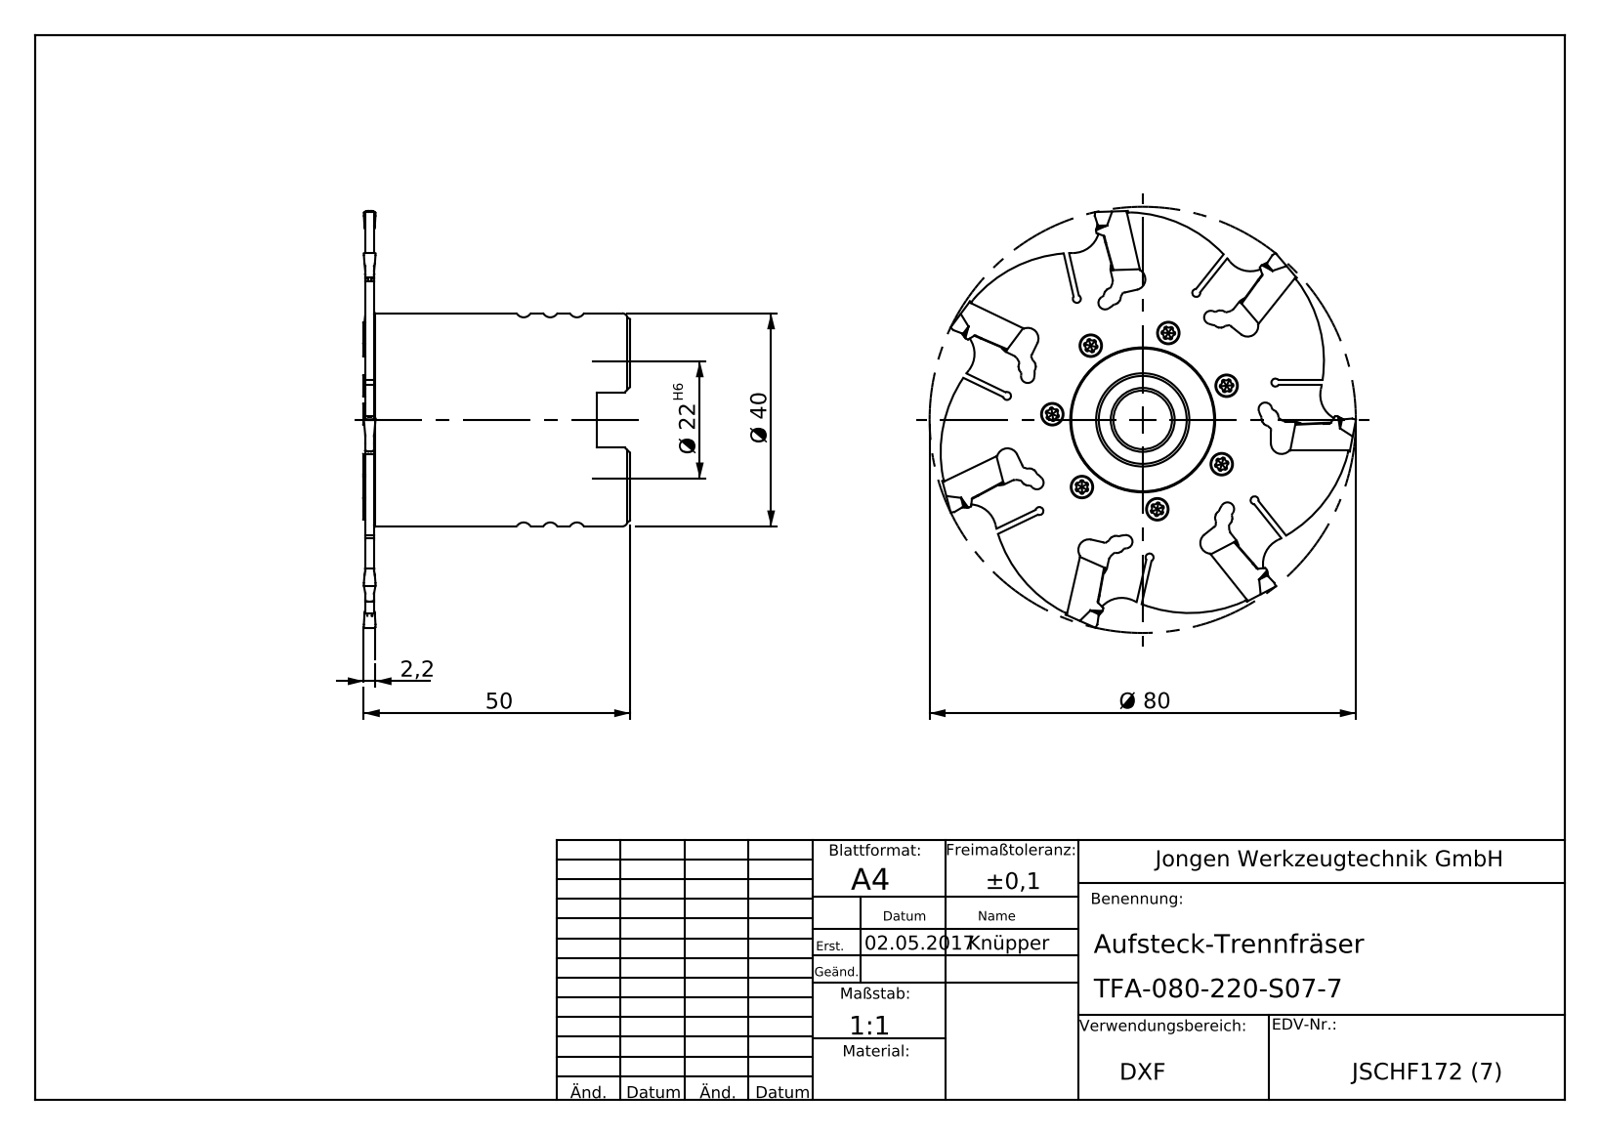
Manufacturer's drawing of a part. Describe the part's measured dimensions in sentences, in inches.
The part is named "TFA-080-220-S07-7; JSCHF172 pk_Kontrolle; JSCHF172_1 pk". Its 3-D file was written by "SolidWorks 2018 (AUTOMOTIVE_DESIGN)". It is 2 solids with 168 faces: 20 planar, 70 cylindrical and 78 other. Overall it measures 3.15 by 3.15 by 1.969 inches. Its volume is 3.448 cubic inches and its surface area 32.88 square inches. Round holes: 7 of diameter 0.098, 7 of diameter 0.126, 7 of diameter 0.165, 1 of diameter 0.433, 1 of diameter 0.65, 1 of diameter 0.866, 1 of diameter 0.872, 1 of diameter 0.878, 1 of diameter 1.063, 1 of diameter 1.685. Round bosses or shafts: 1 of diameter 3.15, 1 of diameter 1.575. The main face-to-face distances are 0.087, 0.077, 0.067, 1.882, 1.892, 1.959, 1.969, 0.787, 1.094, 1.104. The hole center spacings are 0.669, 1.047, 1.305, 0.581, 0.581, 1.306, 0.67, 1.046.
